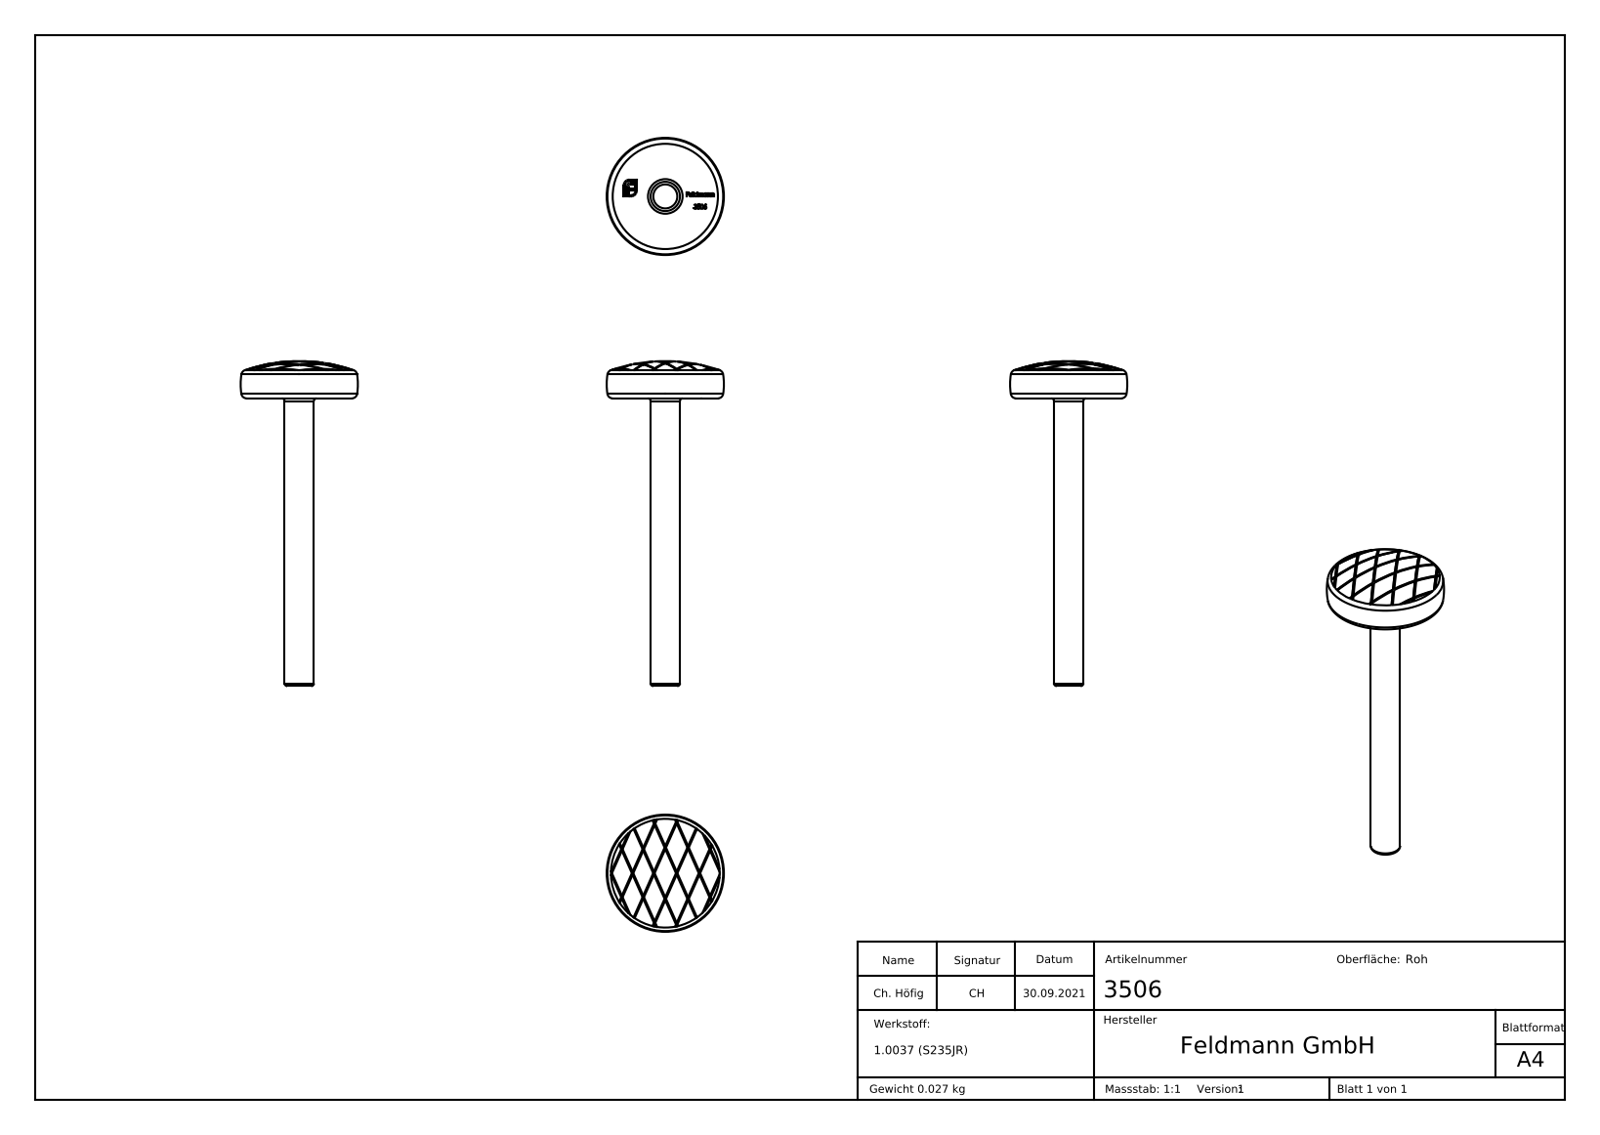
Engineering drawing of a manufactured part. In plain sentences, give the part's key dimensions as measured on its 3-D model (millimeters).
The part is named "3506". Its 3-D file was written by "SolidWorks 2018 (CONFIG_CONTROL_DESIGN)". It is 1 solid with 375 faces: 206 planar, 24 cylindrical and 145 other. Overall it measures 61 by 22 by 22 millimeters. Its volume is 3 521 cubic millimeters and its surface area 2 028 square millimeters. Round bosses or shafts: 1 of diameter 5.5. Partial cylindrical surfaces (rounded edges, fillets, slot ends): 1 of radius 10.2. The main face-to-face distances are 3.91, 3.66, 54, 7.57, 7.82, 11.48, 7.32, 11.23, 4.16, 3.41.
